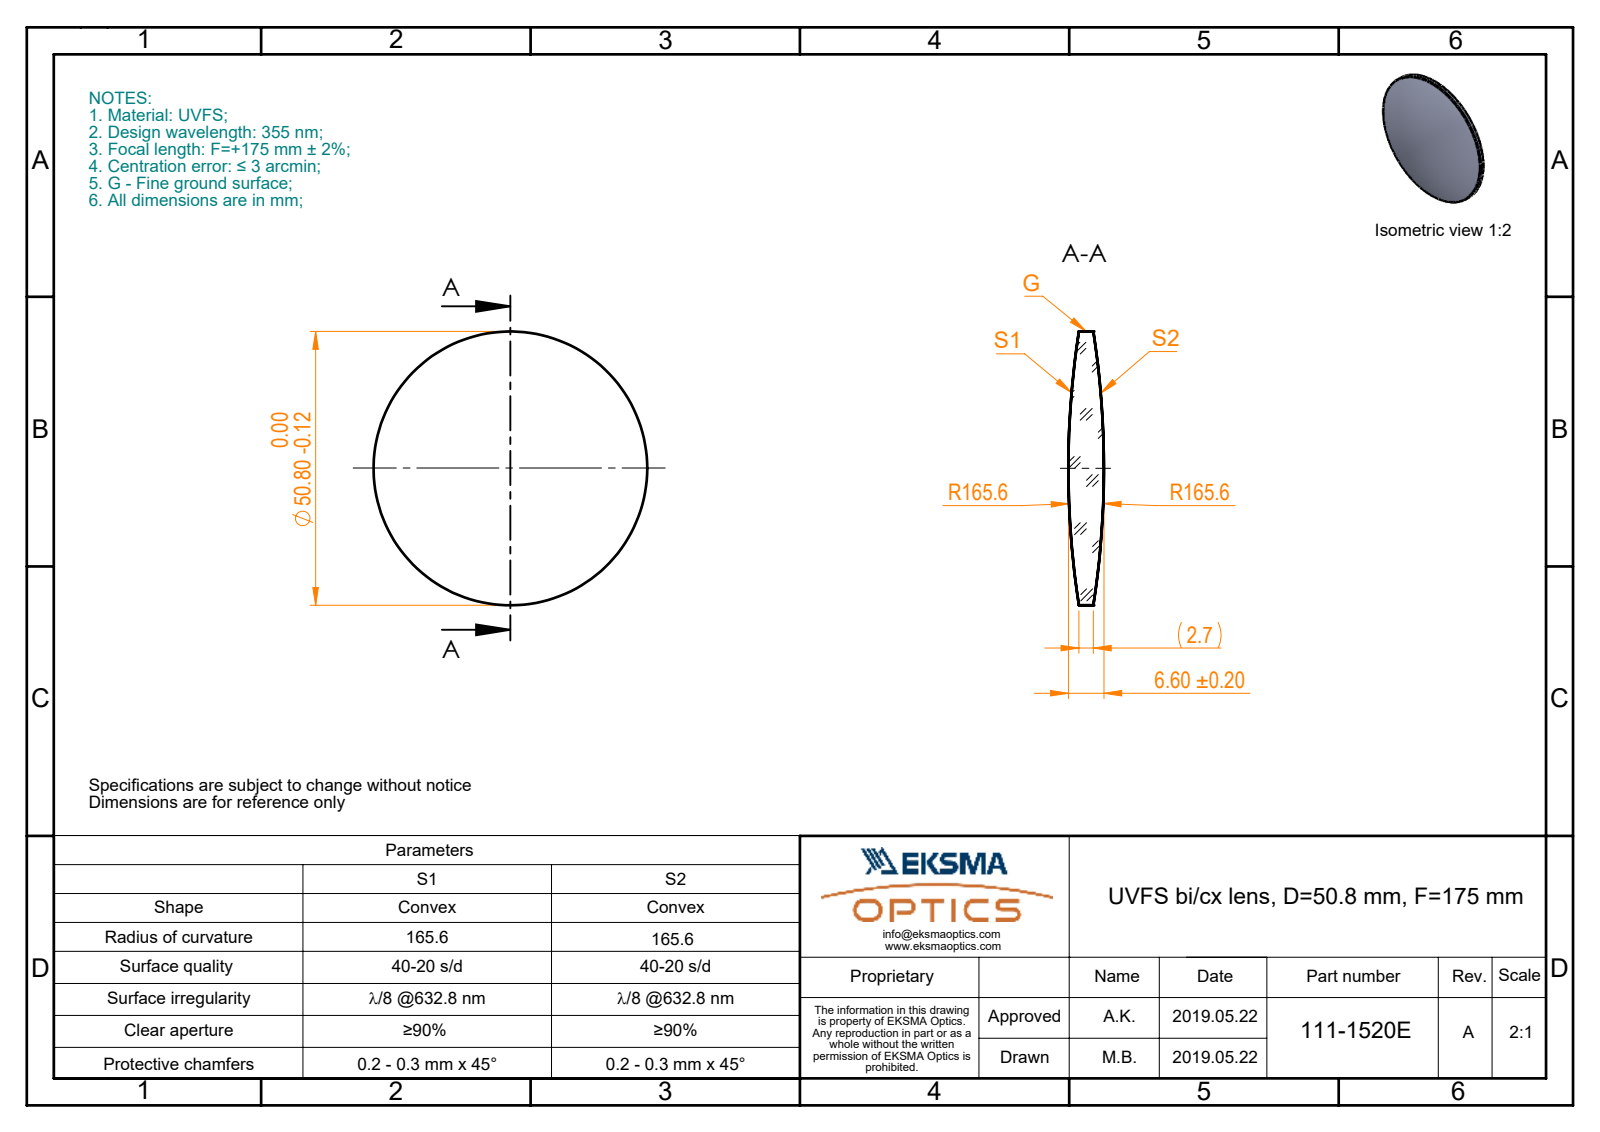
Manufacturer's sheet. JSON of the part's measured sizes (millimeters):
{"part_name": "111-1520E UVFS bi-cx 50.8 F175", "step_written_by": "SolidWorks 2017 (CONFIG_CONTROL_DESIGN)", "units": "millimeters", "bodies": {"solids": 1, "faces": 6, "planar": 0, "cylindrical": 2, "other": 4}, "overall_size": [50.8, 50.8, 6.6], "volume_mm3": 9413, "surface_area_mm2": 4506, "round_bosses_or_shafts": [[50.8, 1]]}
